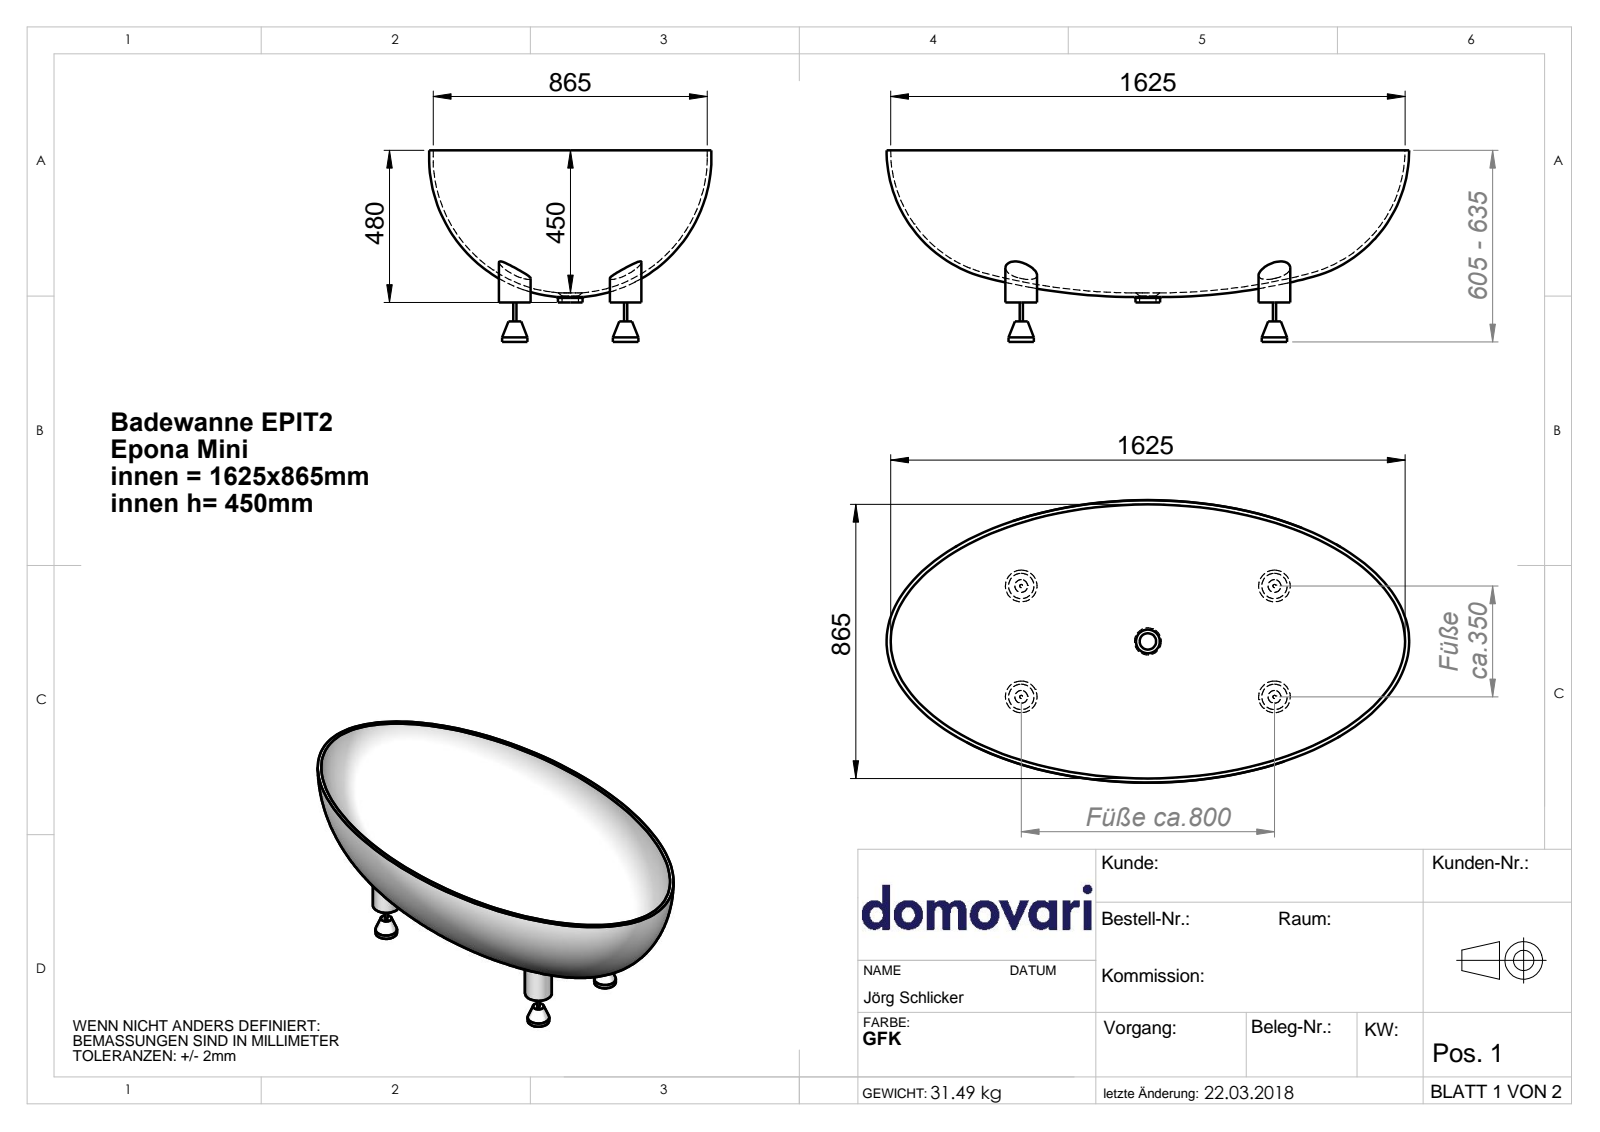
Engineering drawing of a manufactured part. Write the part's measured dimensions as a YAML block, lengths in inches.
part_name: "EPIT2"
step_written_by: "SolidWorks 2017 (AUTOMOTIVE_DESIGN)"
units: inches
bodies: {solids: 2, faces: 69, planar: 23, cylindrical: 24, other: 22}
overall_size: [65, 35.121, 23.819]
volume: 1927
surface_area: 7170
round_bosses_or_shafts:
  - {diameter: 3.937, count: 4}
  - {diameter: 3.15, count: 4}
  - {diameter: 0.394, count: 4}
face_to_face_distances: [0.394, 34.449, 18.504, 18.898, 4.921, 23.425, 23.819, 64.37, 34.843, 34.055]
